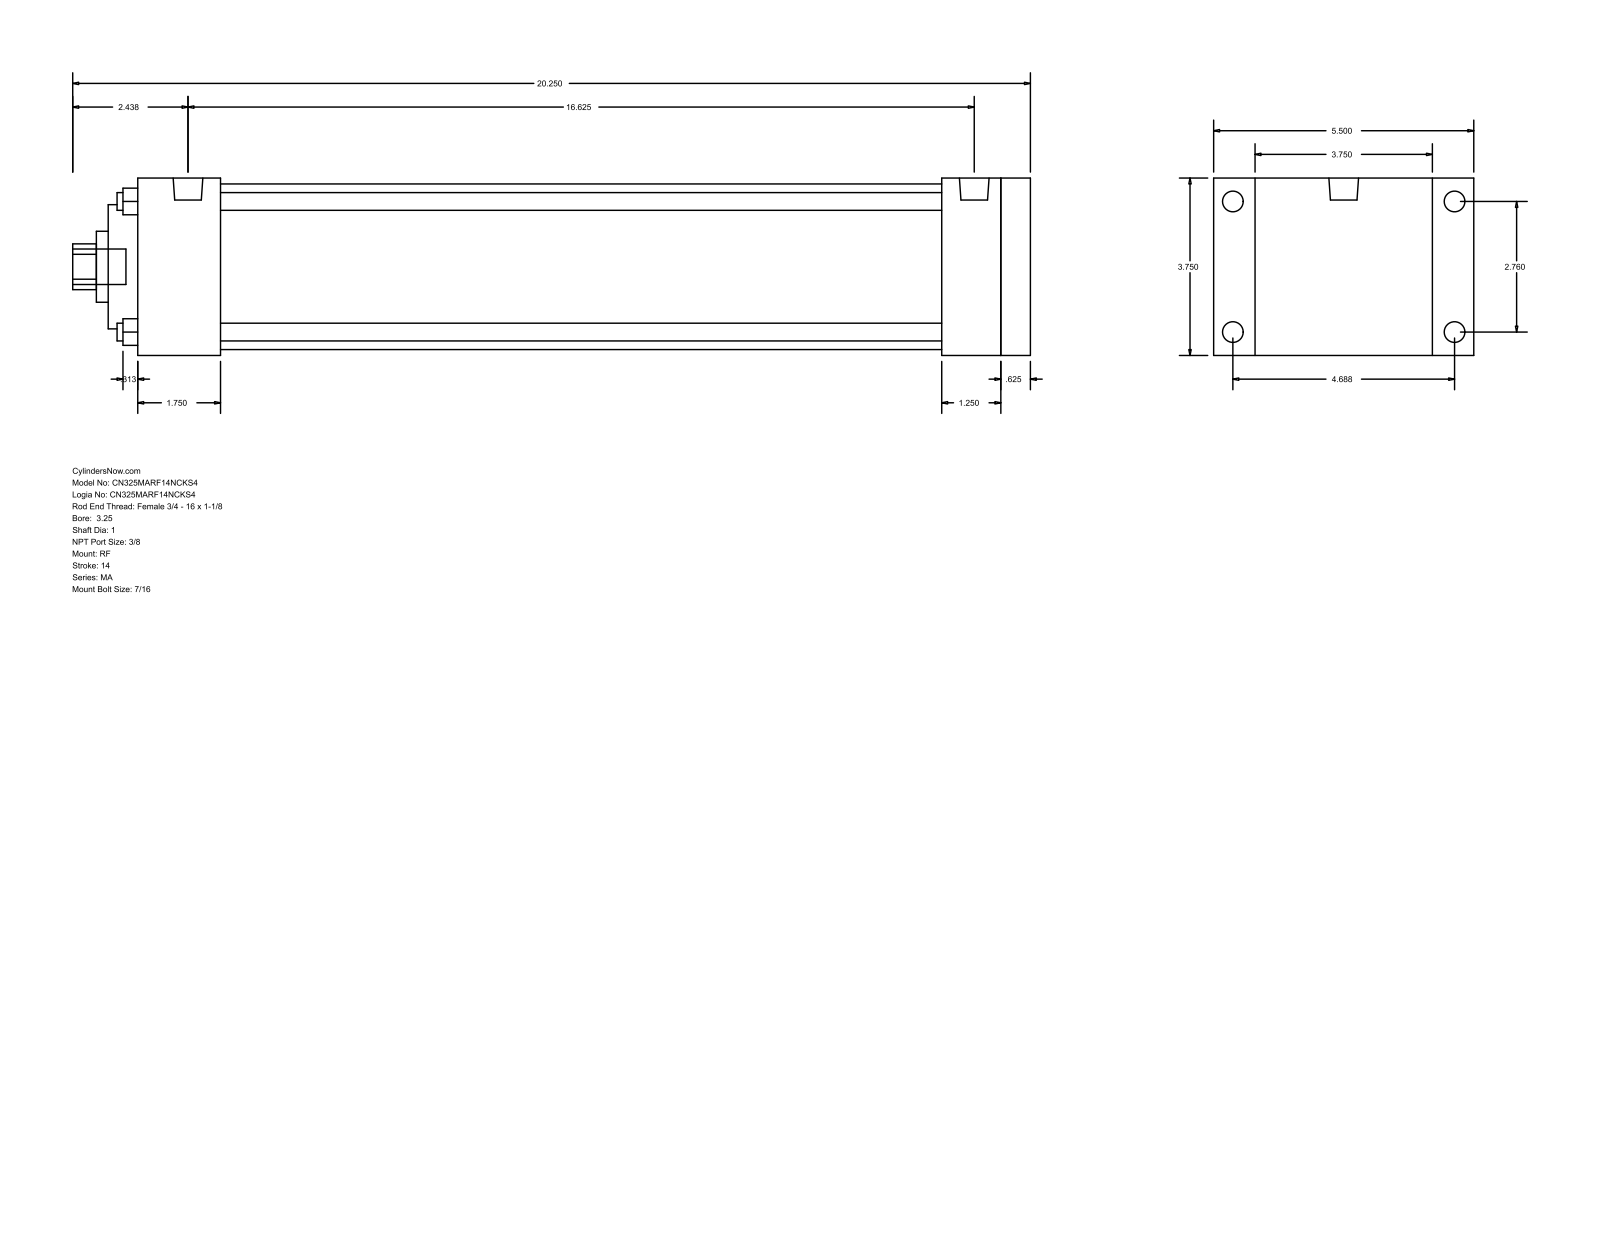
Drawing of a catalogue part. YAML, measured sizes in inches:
part_name: "MA_RF__0325_1"
step_written_by: "GSSL Pune (CONFIG_CONTROL_DESIGN)"
units: inches
bodies: {solids: 0, faces: 94, planar: 65, cylindrical: 29, other: 0}
overall_size: [20.25, 5.5, 3.75]
round_holes:
  - {diameter: 0.375, count: 4}
  - {diameter: 1, count: 1}
  - {diameter: 1.5, count: 1}
  - {diameter: 2.625, count: 1}
  - {diameter: 3.5, count: 1}
round_bosses_or_shafts:
  - {diameter: 0.437, count: 8}
  - {diameter: 0.627, count: 2}
  - {diameter: 0.75, count: 1}
partial_cylinders:
  - {radius: 0.484, count: 1}
face_to_face_distances: [3.75, 18.875, 0.625, 18.25, 0.875, 4.625, 17, 1.25, 1.875, 1.75]
hole_center_spacings: [1.952, 2.76, 3.903]
